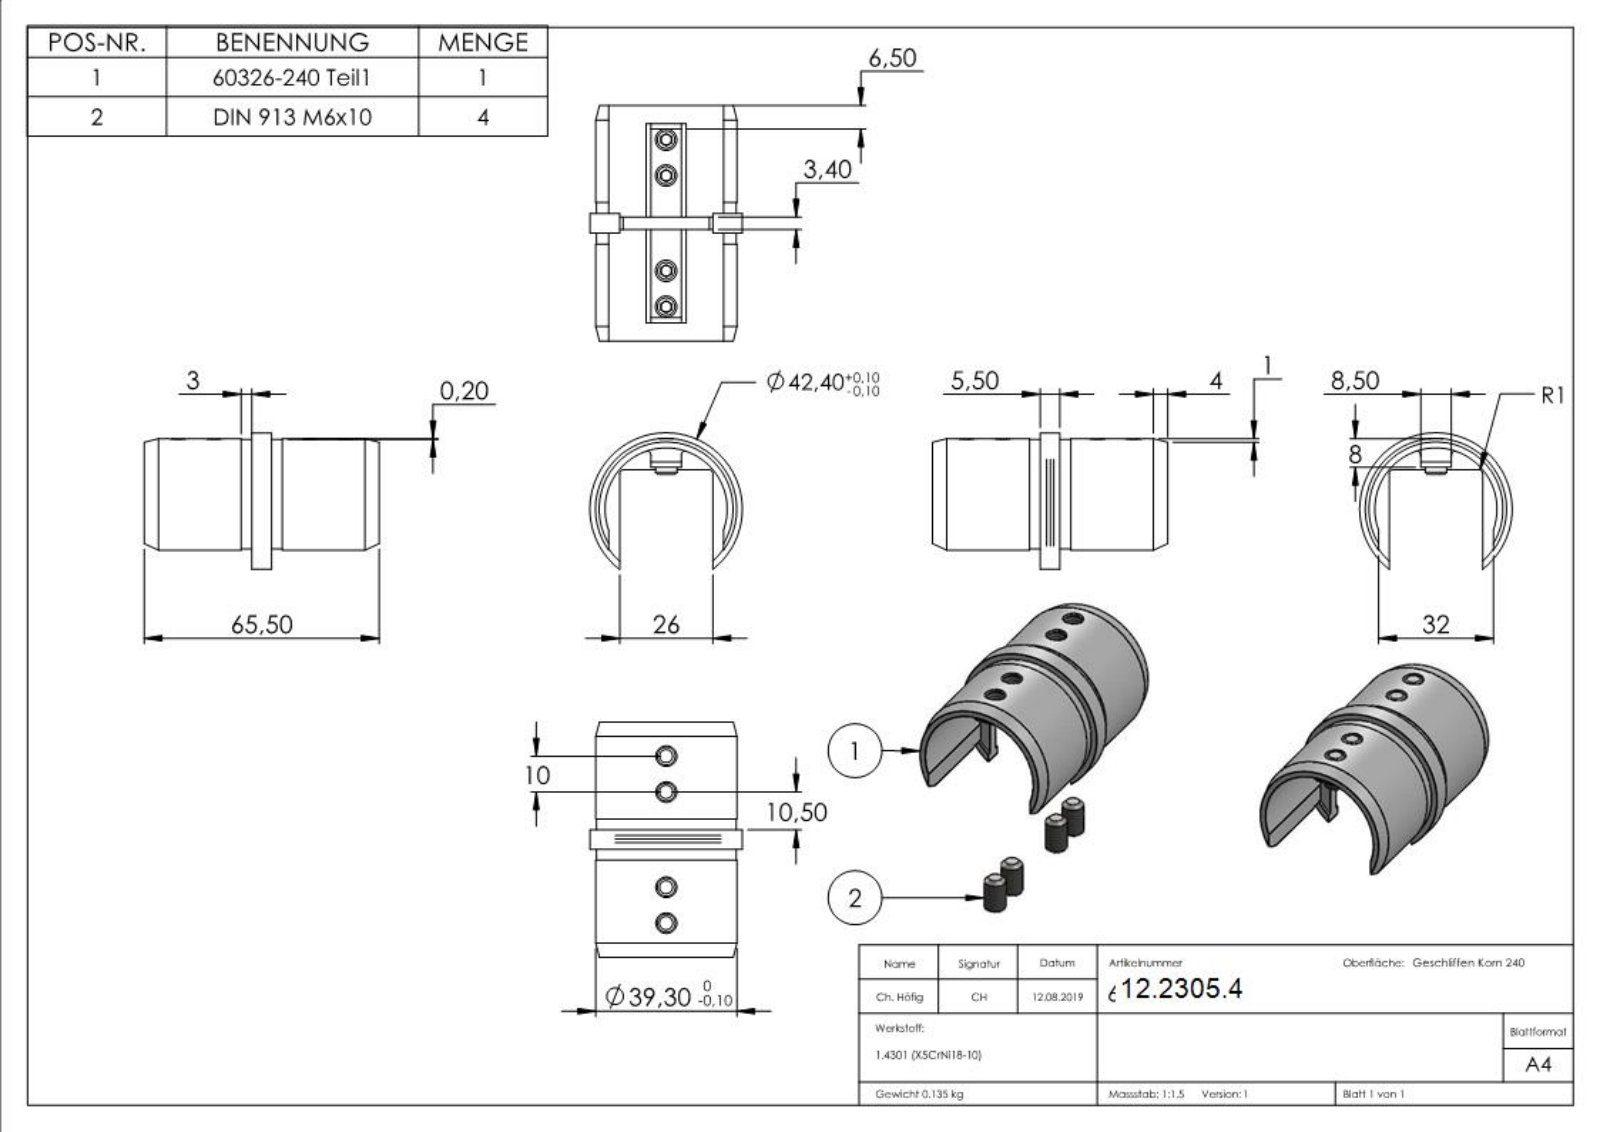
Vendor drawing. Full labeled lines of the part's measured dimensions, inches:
Part name (STEP PRODUCT): DIN913_DIN 913 M6x10; 6032X-240 Teil1_60326-240 Teil1; 60326-240
STEP written by: SolidWorks 2015 (CONFIG_CONTROL_DESIGN)
Units: inches
Bodies: 5 solids, 391 faces (198 planar, 45 cylindrical, 148 other)
Overall size (bounding box): 2.579 × 1.669 × 1.494
Volume: 1.045 in³ · Surface area: 21.16 in²
Round holes (diameter × count): ⌀0.197 ×4
Round bosses / shafts (diameter × count): ⌀0.236 ×4
Partial cylindrical surfaces — rounded edges, fillets, slot ends (radius × count): R0.039 ×4, R0.669 ×1, R0.766 ×1, R0.774 ×1, R0.835 ×1
Main face-to-face distances: 0.463, 0.797, 0.041, 0.175, 1.26, 0.118, 1.181, 1.222, 1.356, 1.398
Hole centre spacings: 0.394, 1.437, 1.043, 1.831
